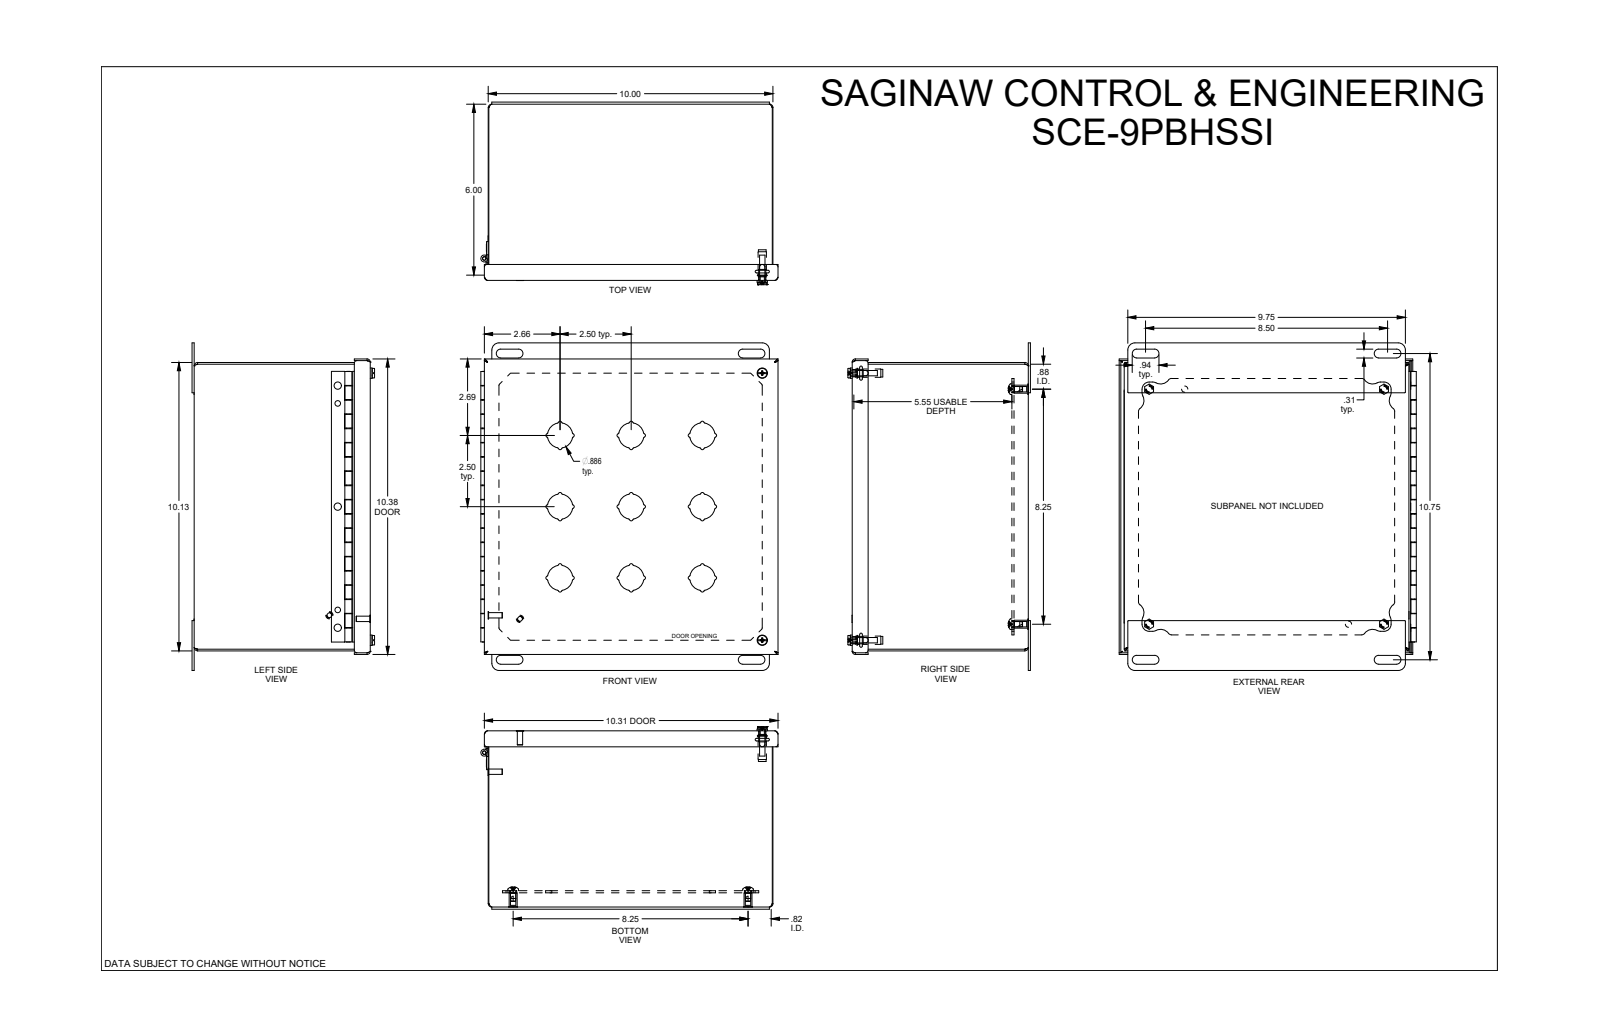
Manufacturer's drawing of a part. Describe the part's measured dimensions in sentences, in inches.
The part is named "SCE-9PBHSSI". Its 3-D file was written by "SolidWorks 2021 (AUTOMOTIVE_DESIGN)". It is 23 solids with 1009 faces: 423 planar, 379 cylindrical and 207 other. Overall it measures 11.5 by 10.563 by 6.411 inches. Its volume is 40.64 cubic inches and its surface area 1 235 square inches. Round holes: 6 of diameter 0.19, 6 of diameter 0.25, 5 of diameter 0.193, 4 of diameter 0.281, 4 of diameter 0.317, 2 of diameter 0.126, 2 of diameter 0.218, 2 of diameter 0.22, 2 of diameter 0.266. Round bosses or shafts: 11 of diameter 0.188, 5 of diameter 0.256, 4 of diameter 0.437, 4 of diameter 0.373, 4 of diameter 0.28, 2 of diameter 0.362, 2 of diameter 0.34, 2 of diameter 0.334. Partial cylindrical surfaces (rounded edges, fillets, slot ends): 72 of radius 0.04, 36 of radius 0.062, 33 of radius 0.443, 20 of radius 0.06, 16 of radius 0.25, 8 of radius 0.063, 8 of radius 0.125, 8 of radius 0.156. The main face-to-face distances are 0.06, 6.125, 10.065, 9.94, 6.065, 6.185, 0.5, 5.625, 0.515, 0.575. The hole center spacings are 0.752, 8.702, 8.893, 12.419, 0.125, 0.625, 1.25, 3.625.
